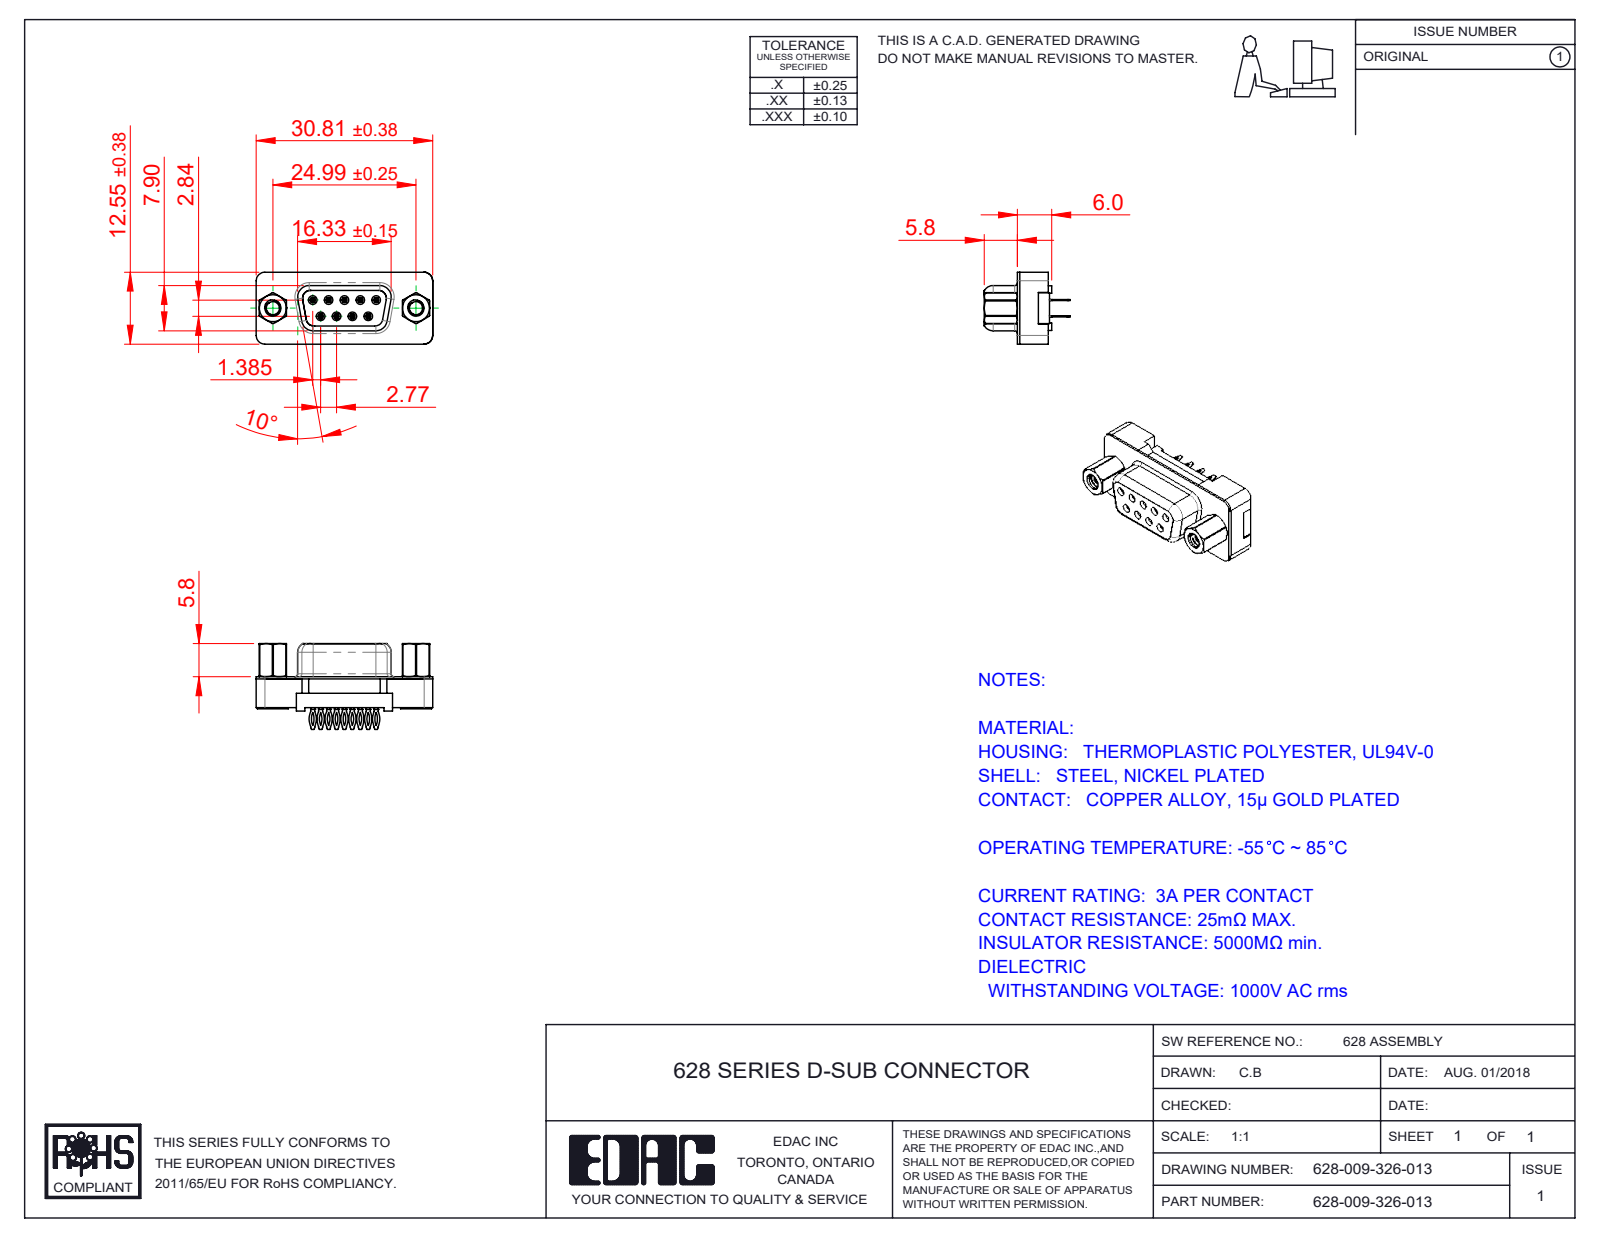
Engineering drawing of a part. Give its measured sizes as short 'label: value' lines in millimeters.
name: 628-009-326-013; 628 Plastic Body Housing_09 Contacts; 628 PB Contact Row 1_26; 628 PB Contact Row 2_26 (+3 more)
written by: SolidWorks 2020 (CONFIG_CONTROL_DESIGN)
unit: mm
bodies: 15 solids, 1181 faces (454 planar, 356 cylindrical, 371 other)
size: 30.82 × 15 × 12.55
volume: 2 170 mm³; area: 4 837 mm²
holes: 9× ⌀0.9, 2× ⌀2.26, 2× ⌀2.29, 2× ⌀3.05, 2× ⌀4, 2× ⌀4.8, 2× ⌀5
bosses: 2× ⌀4.9, 2× ⌀2.79
rounds: 36× R0.25, 18× R2.92, 18× R3.33, 13× R0.5, 11× R1.35, 9× R0.3, 8× R1.5, 4× R0.9
face distances: 0.4, 2, 5.54, 2.77, 2.5, 5, 6.2, 5.4, 8.7, 7.54
hole spacings: 3.16, 2.77, 5.54, 5.03, 5.04, 8.31, 7.1, 7.48
